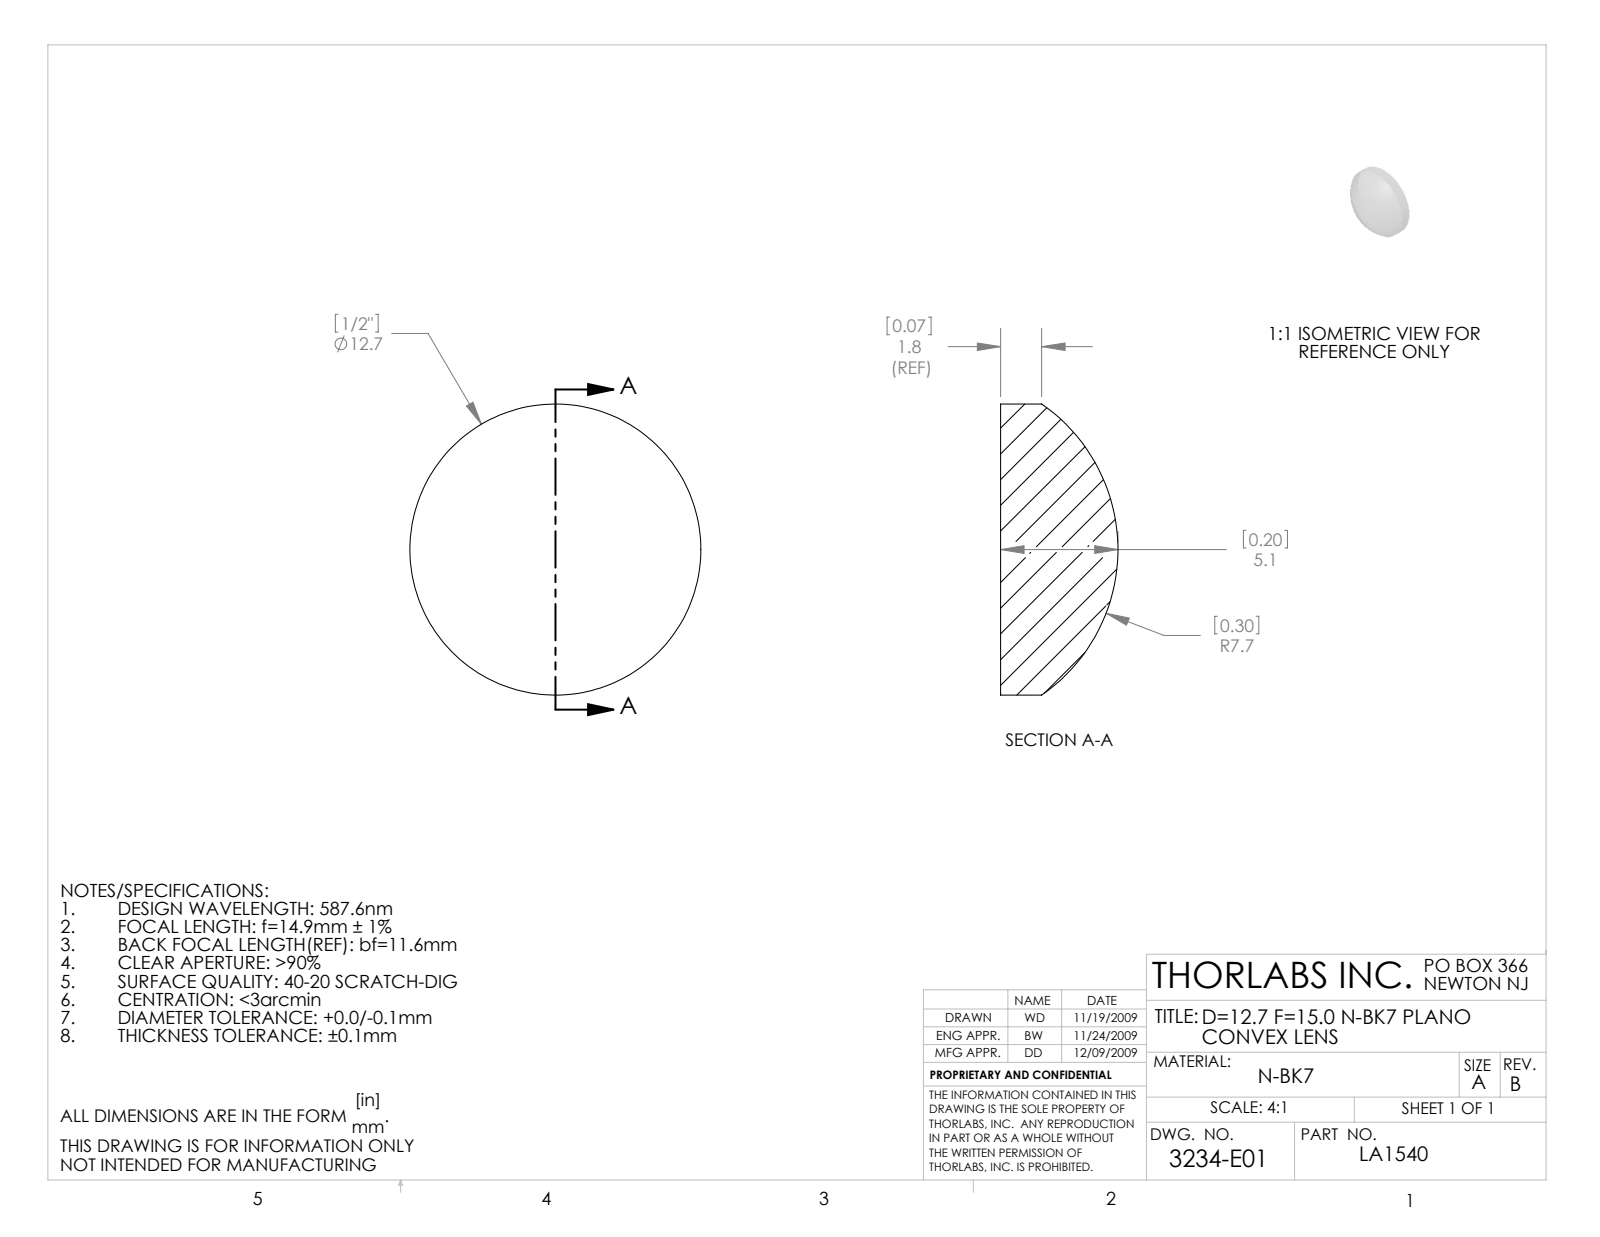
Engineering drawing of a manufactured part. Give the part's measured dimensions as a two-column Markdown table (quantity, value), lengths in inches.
| quantity | value |
| --- | --- |
| part name | 3234-E0W |
| STEP written by | SolidWorks 2009 (AUTOMOTIVE_DESIGN) |
| units | inches |
| bodies | 1 solid, 5 faces (1 planar, 2 cylindrical, 2 other) |
| overall size | 0.5 × 0.5 × 0.202 |
| volume | 0.028 in³ |
| surface area | 0.558 in² |
| round bosses / shafts (diameter × count) | 0.5 × 1 |
